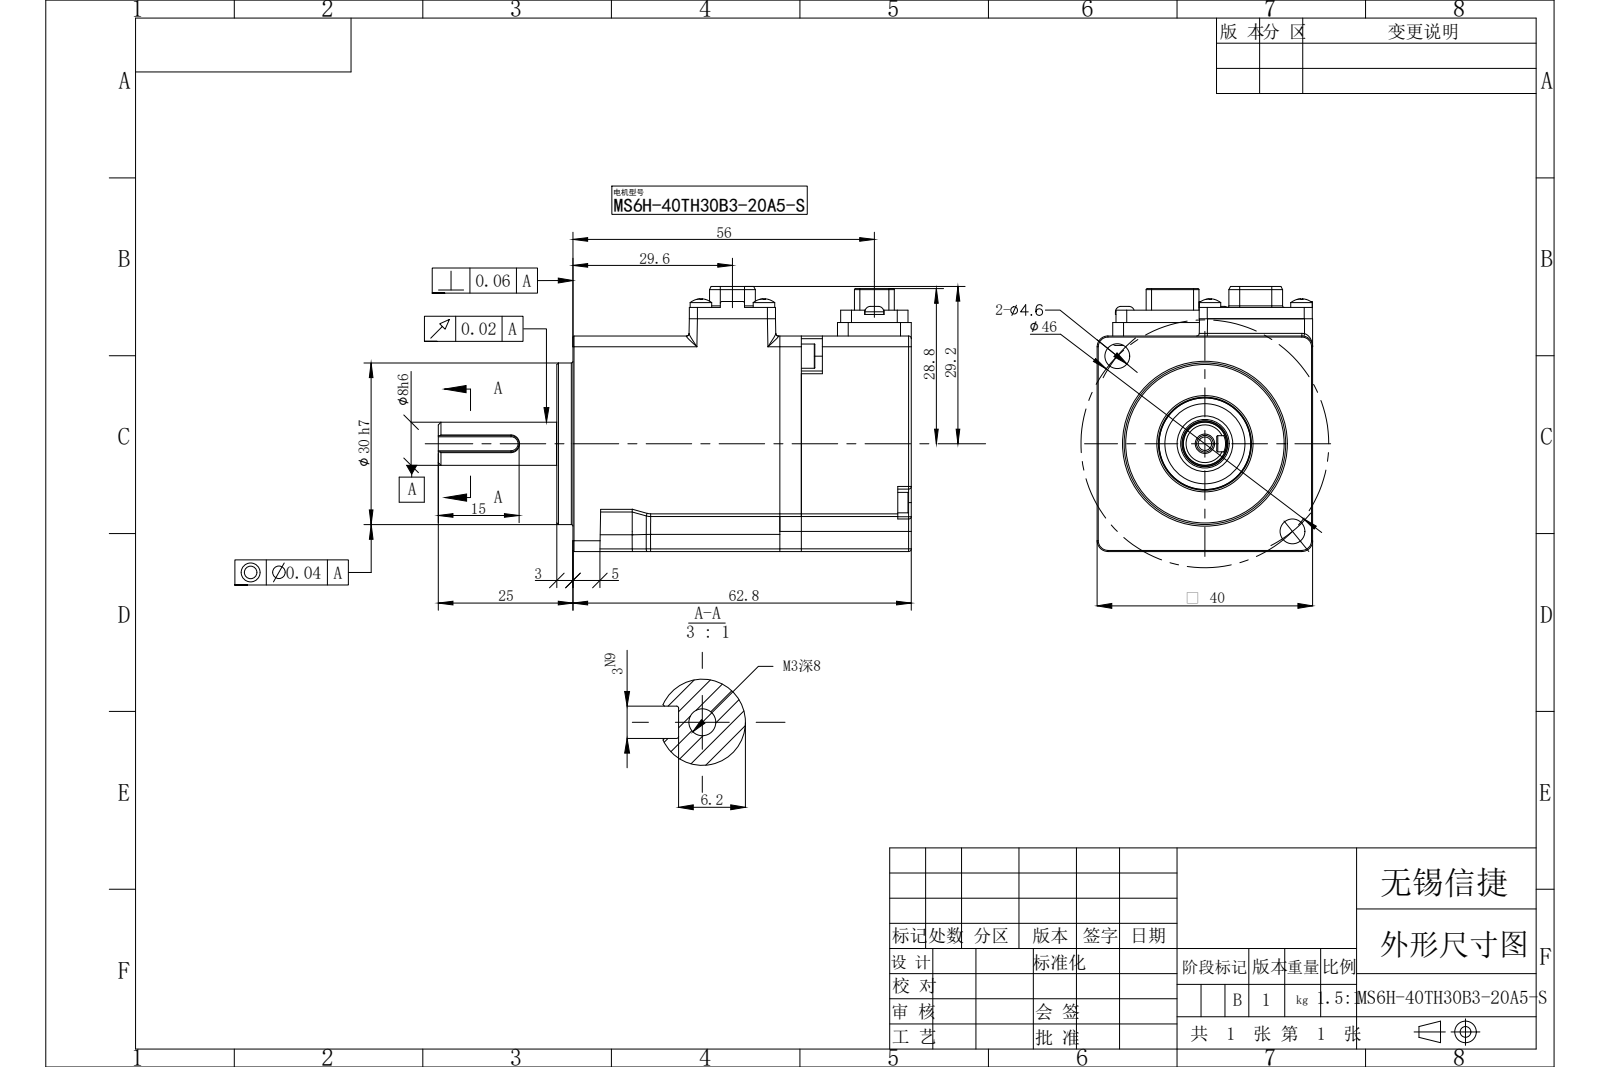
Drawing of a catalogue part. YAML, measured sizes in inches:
part_name: "MS6H-40TH30B3-20A5-S"
step_written_by: "SolidWorks 2022 (CONFIG_CONTROL_DESIGN)"
units: inches
bodies: {solids: 0, faces: 711, planar: 386, cylindrical: 210, other: 115}
overall_size: [3.457, 1.937, 1.575]
round_holes:
  - {diameter: 0.083, count: 4}
  - {diameter: 0.063, count: 2}
  - {diameter: 0.181, count: 2}
  - {diameter: 0.098, count: 1}
  - {diameter: 0.354, count: 1}
  - {diameter: 0.585, count: 1}
round_bosses_or_shafts:
  - {diameter: 0.157, count: 4}
  - {diameter: 0.15, count: 4}
  - {diameter: 0.177, count: 2}
  - {diameter: 0.138, count: 2}
  - {diameter: 1.181, count: 1}
  - {diameter: 0.669, count: 1}
  - {diameter: 0.407, count: 1}
  - {diameter: 0.335, count: 1}
partial_cylinders:
  - {radius: 0.02, count: 58}
  - {radius: 0.008, count: 19}
  - {radius: 0.079, count: 16}
  - {radius: 0.012, count: 10}
  - {radius: 0.059, count: 9}
  - {radius: 0.039, count: 4}
  - {radius: 0.098, count: 4}
  - {radius: 0.118, count: 4}
face_to_face_distances: [1.575, 2.472, 0.803, 1.669, 0.256, 1.319, 0.118, 2.591, 1.787, 0.157]
hole_center_spacings: [0.315, 0.654, 0.726, 0.906, 0.669, 0.881, 1.065, 1.074]
